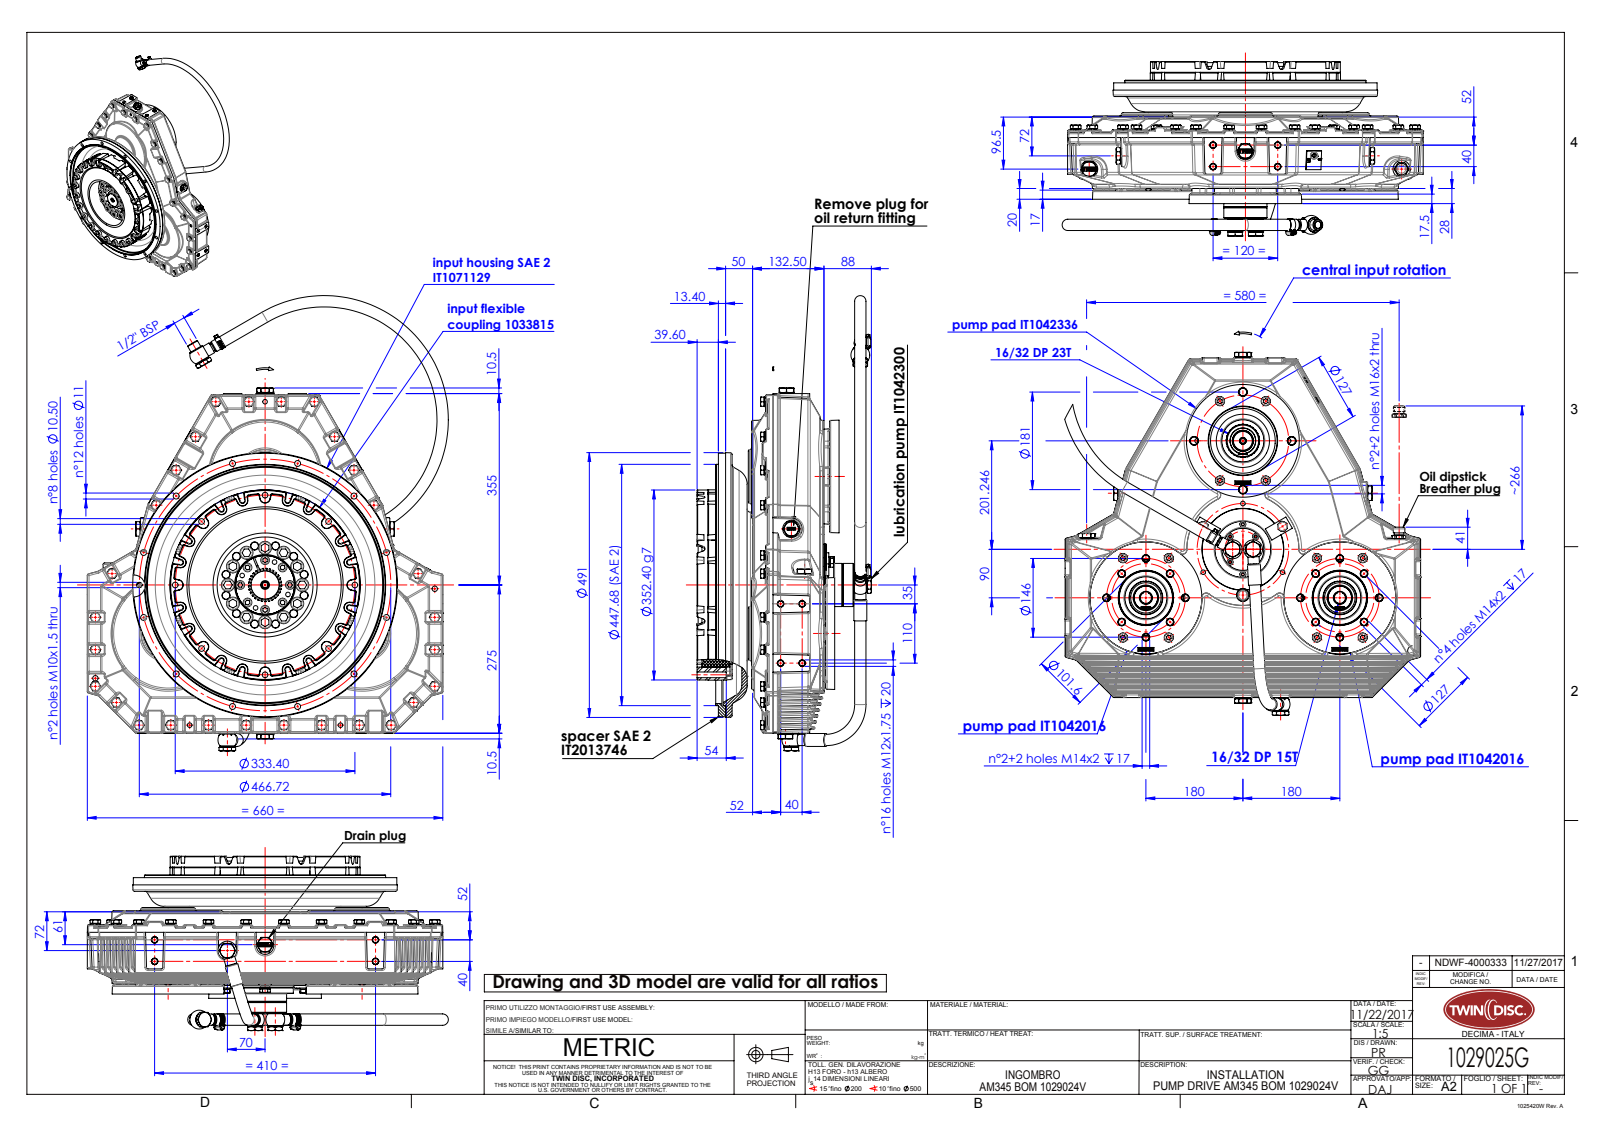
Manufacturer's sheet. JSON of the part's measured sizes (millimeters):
{"part_name": "IT2021216_rev03-installation; IT4588040_rev00-installation; IT1042016_rev00-installation; IT1042336_rev01-installation_reissued (+8 more)", "step_written_by": "SolidWorks 2015 (AUTOMOTIVE_DESIGN)", "units": "millimeters", "bodies": {"solids": 102, "faces": 10352, "planar": 4578, "cylindrical": 2722, "other": 3052}, "overall_size": [844.88, 670.16, 323.5], "volume_mm3": 11990000, "surface_area_mm2": 3892000, "round_holes": [[10.2, 52], [8.5, 49], [14, 44], [10.5, 38], [11, 33], [12, 29], [17, 24], [13, 15], [8, 10], [10, 10], [21, 9], [10.92, 8]], "round_bosses_or_shafts": [[10, 61], [18.1, 33], [16.2, 33], [16, 32], [24, 14], [18, 11], [21.1, 7], [12, 7]], "partial_cylinders_radius": [[3, 369], [2, 126], [5, 98], [2.54, 72], [0.45, 58], [1.5, 48], [1.54, 48], [9.4, 24]], "face_to_face_distances": [152.5, 8, 30, 5, 48, 10, 20, 18, 3, 28], "hole_center_spacings": [57.4, 120, 138.58, 40, 207.84, 51.37, 66.61, 85.42]}
